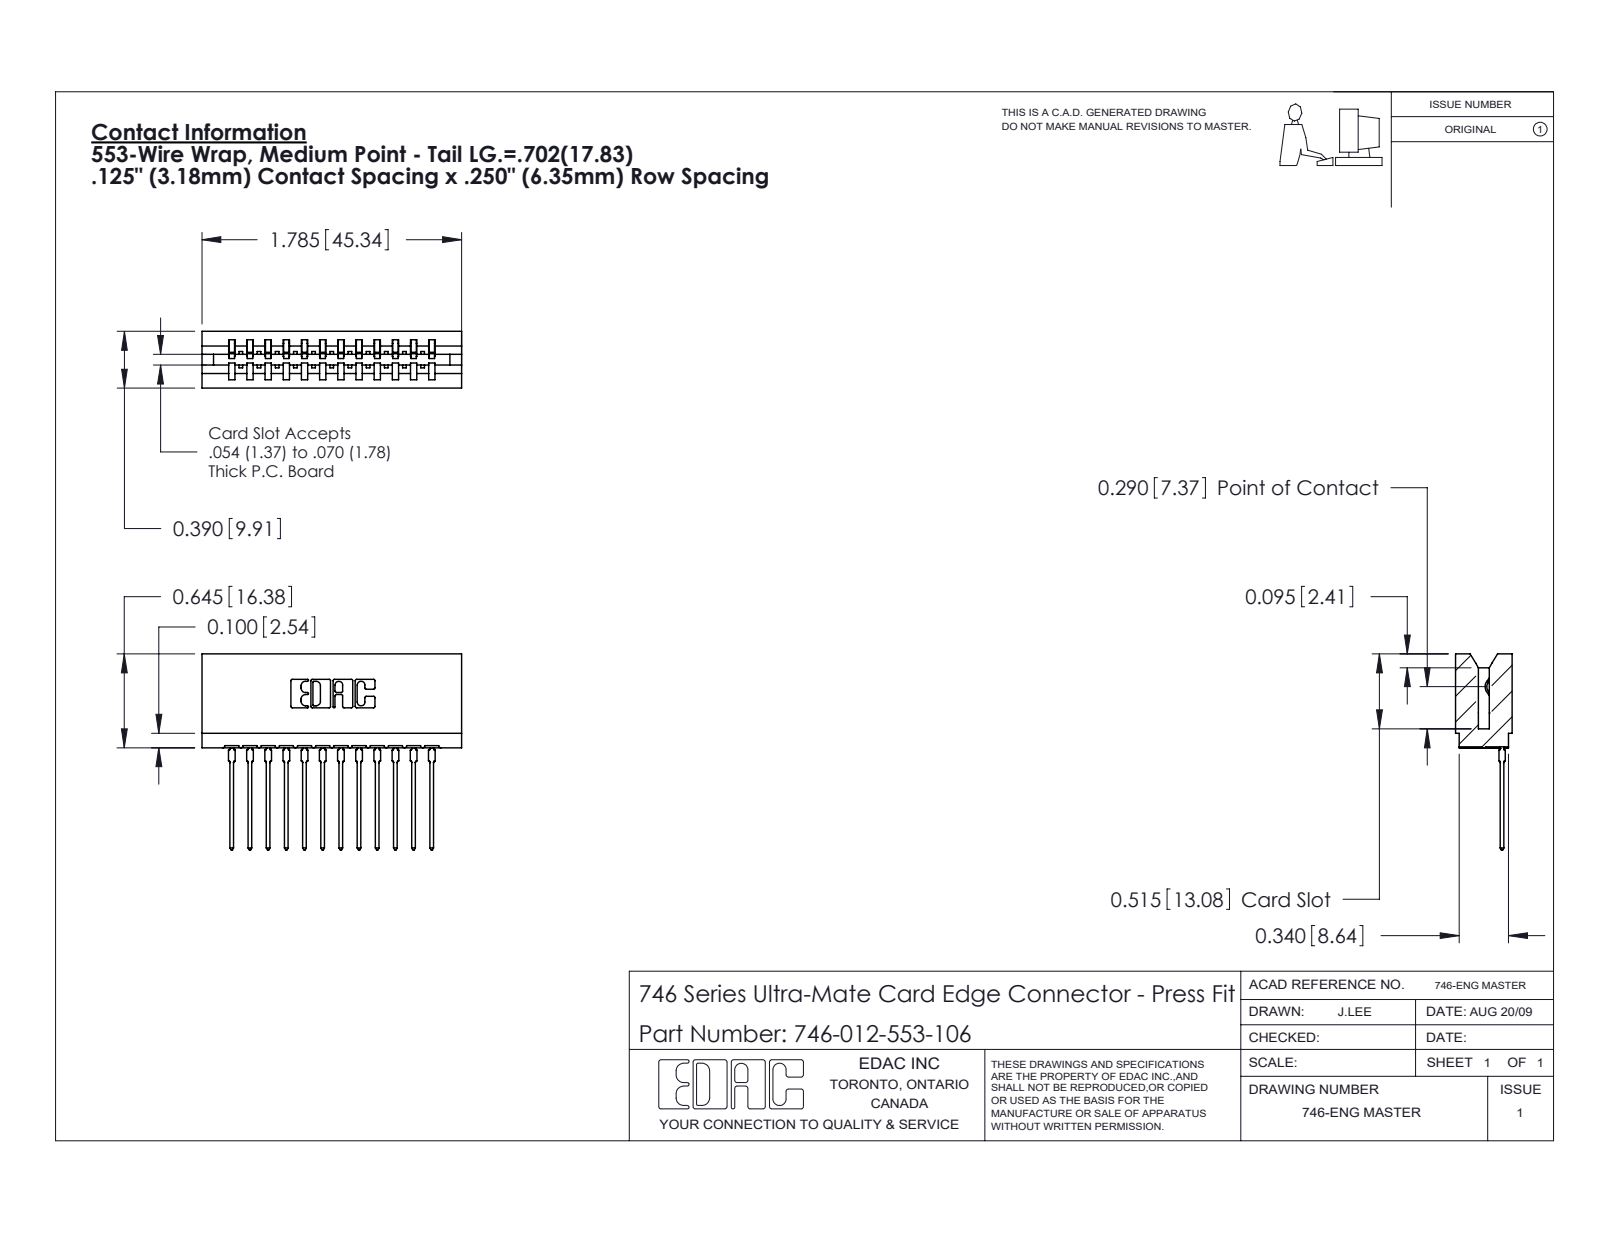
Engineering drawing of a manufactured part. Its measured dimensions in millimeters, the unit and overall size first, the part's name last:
Units: millimetres
Overall size (bounding box): 45.3 × 34.2 × 9.9
Partial cylindrical surfaces — rounded edges, fillets, slot ends (radius × count): R0.5 ×24, R0.3 ×22, R0.4 ×13, R0.2 ×6, R0.8 ×6, R0.1 ×4, R0.3 ×4, R0.7 ×3
Main face-to-face distances: 6.4, 8.5, 1.4, 12.7, 3.2, 3.2, 9.9, 1.1, 5.3, 11.6
Volume: 4 970 mm³ · Surface area: 7 090 mm²
Bodies: 13 solids, 1394 faces (812 planar, 270 cylindrical, 312 other)
Part name (STEP PRODUCT): 746-292-001_553; 746-012-553-106; 746 Part_.515 Slot Depth - 06
STEP written by: SolidWorks 2020 (CONFIG_CONTROL_DESIGN)
